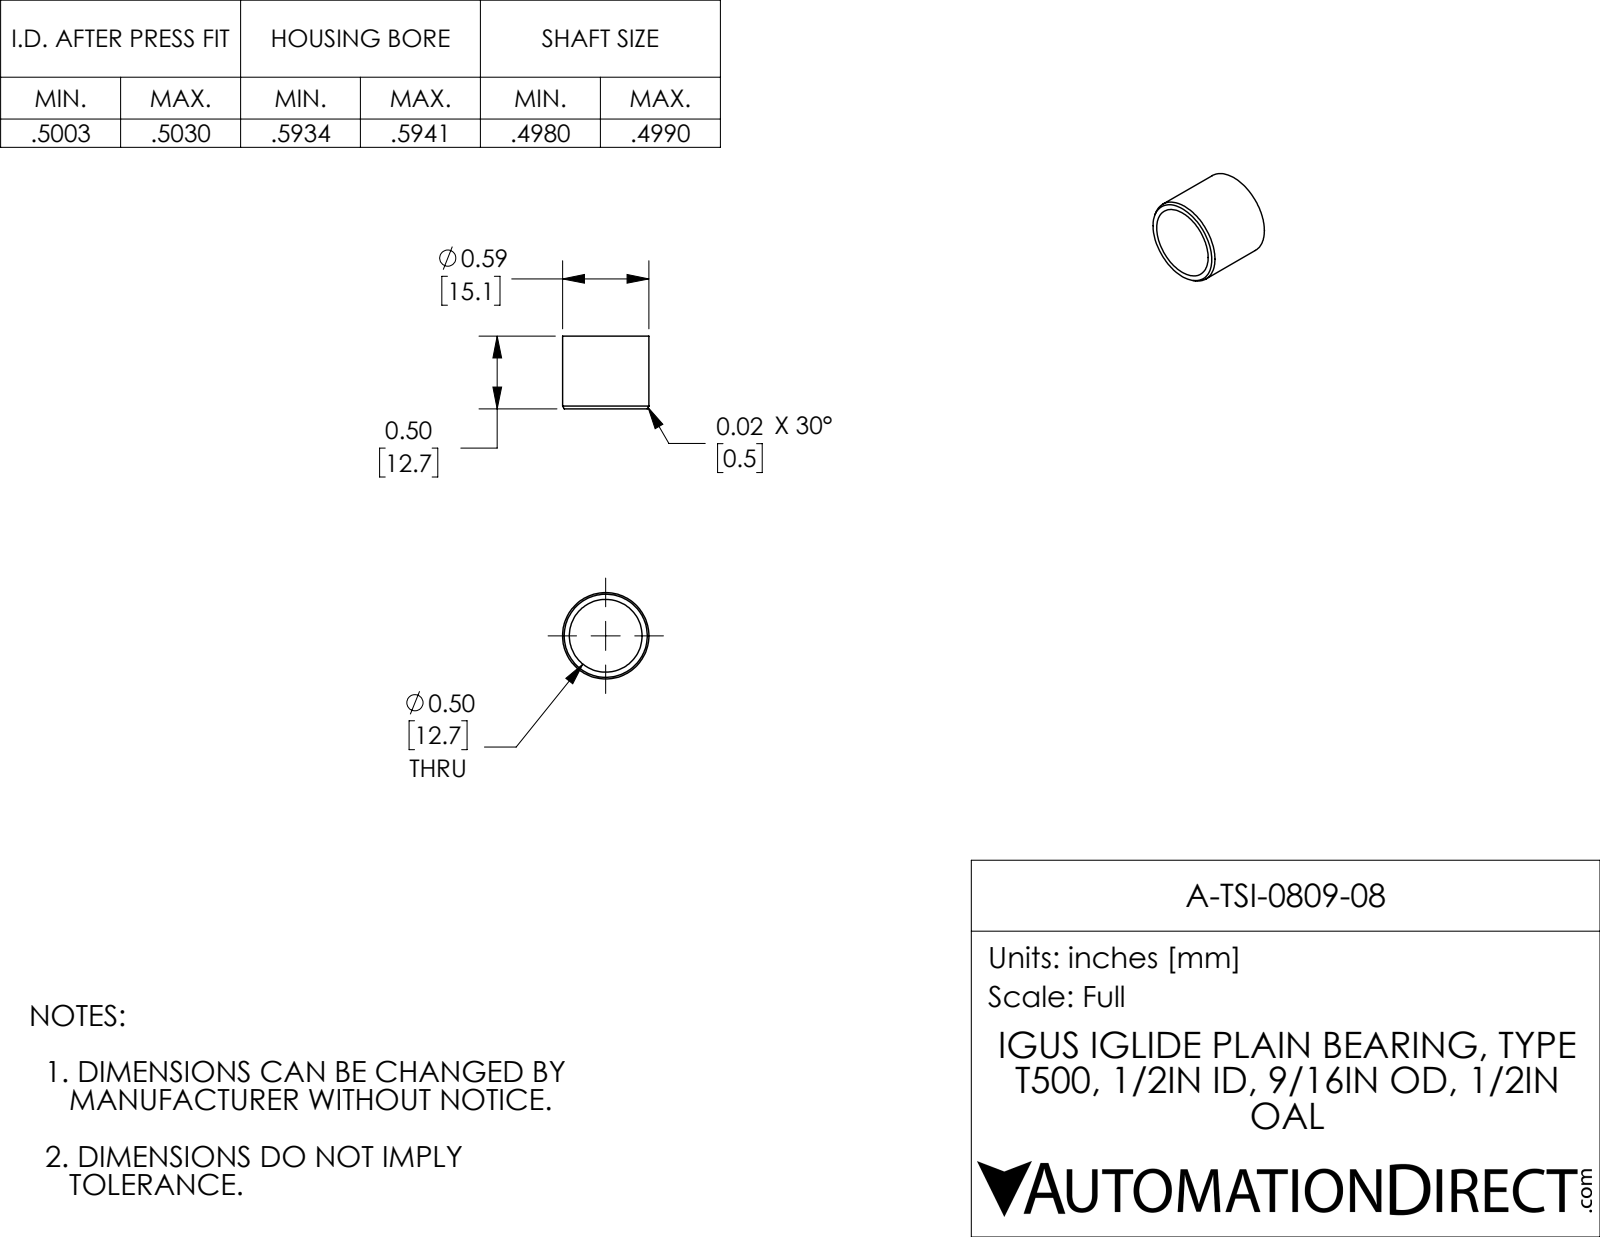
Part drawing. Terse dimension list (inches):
name: A-TSI-0809-08
written by: SolidWorks 2017 (AUTOMOTIVE_DESIGN)
unit: in
bodies: 1 solid, 10 faces (2 planar, 4 cylindrical, 4 other)
size: 0.594 × 0.594 × 0.5
volume: 0.04 in³; area: 1.851 in²
holes: 1× ⌀0.5
bosses: 1× ⌀0.594
face distances: 0.5
